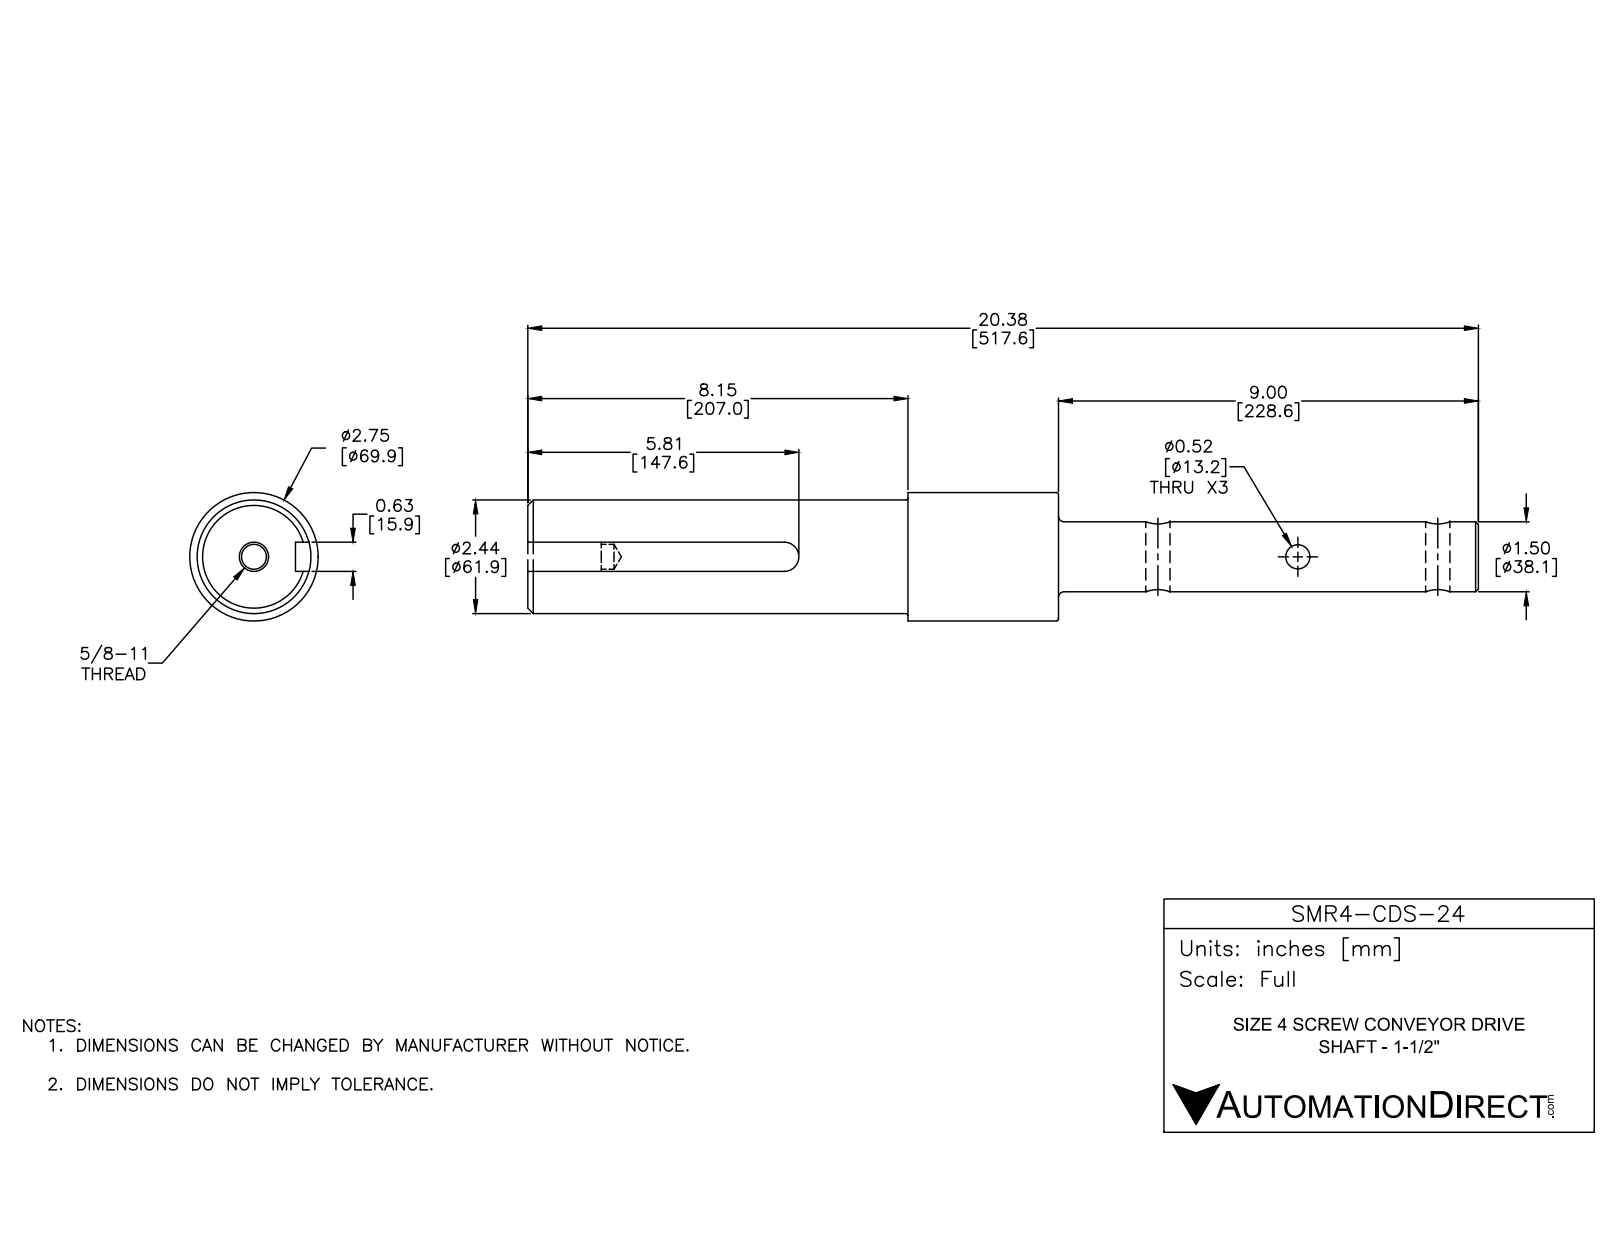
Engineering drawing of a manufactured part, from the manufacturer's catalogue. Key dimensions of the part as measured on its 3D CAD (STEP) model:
Part name (STEP PRODUCT): SMR4-CDS-24
STEP written by: SolidWorks 2016 (AUTOMOTIVE_DESIGN)
Units: inches
Bodies: 1 solid, 38 faces (8 planar, 18 cylindrical, 12 other)
Overall size (bounding box): 20.378 × 2.75 × 2.75
Volume: 70.43 in³ · Surface area: 156.1 in²
Round holes (diameter × count): ⌀0.52 ×3, ⌀0.531 ×1, ⌀0.625 ×1
Round bosses / shafts (diameter × count): ⌀2.75 ×1, ⌀2.437 ×1, ⌀1.5 ×1
Partial cylindrical surfaces — rounded edges, fillets, slot ends (radius × count): R0.312 ×1
Main face-to-face distances: 11.378, 0.625, 20.378, 9, 8.15, 3.228, 12.228, 1.575, 6.575, 9.803
Hole centre spacings: 6
